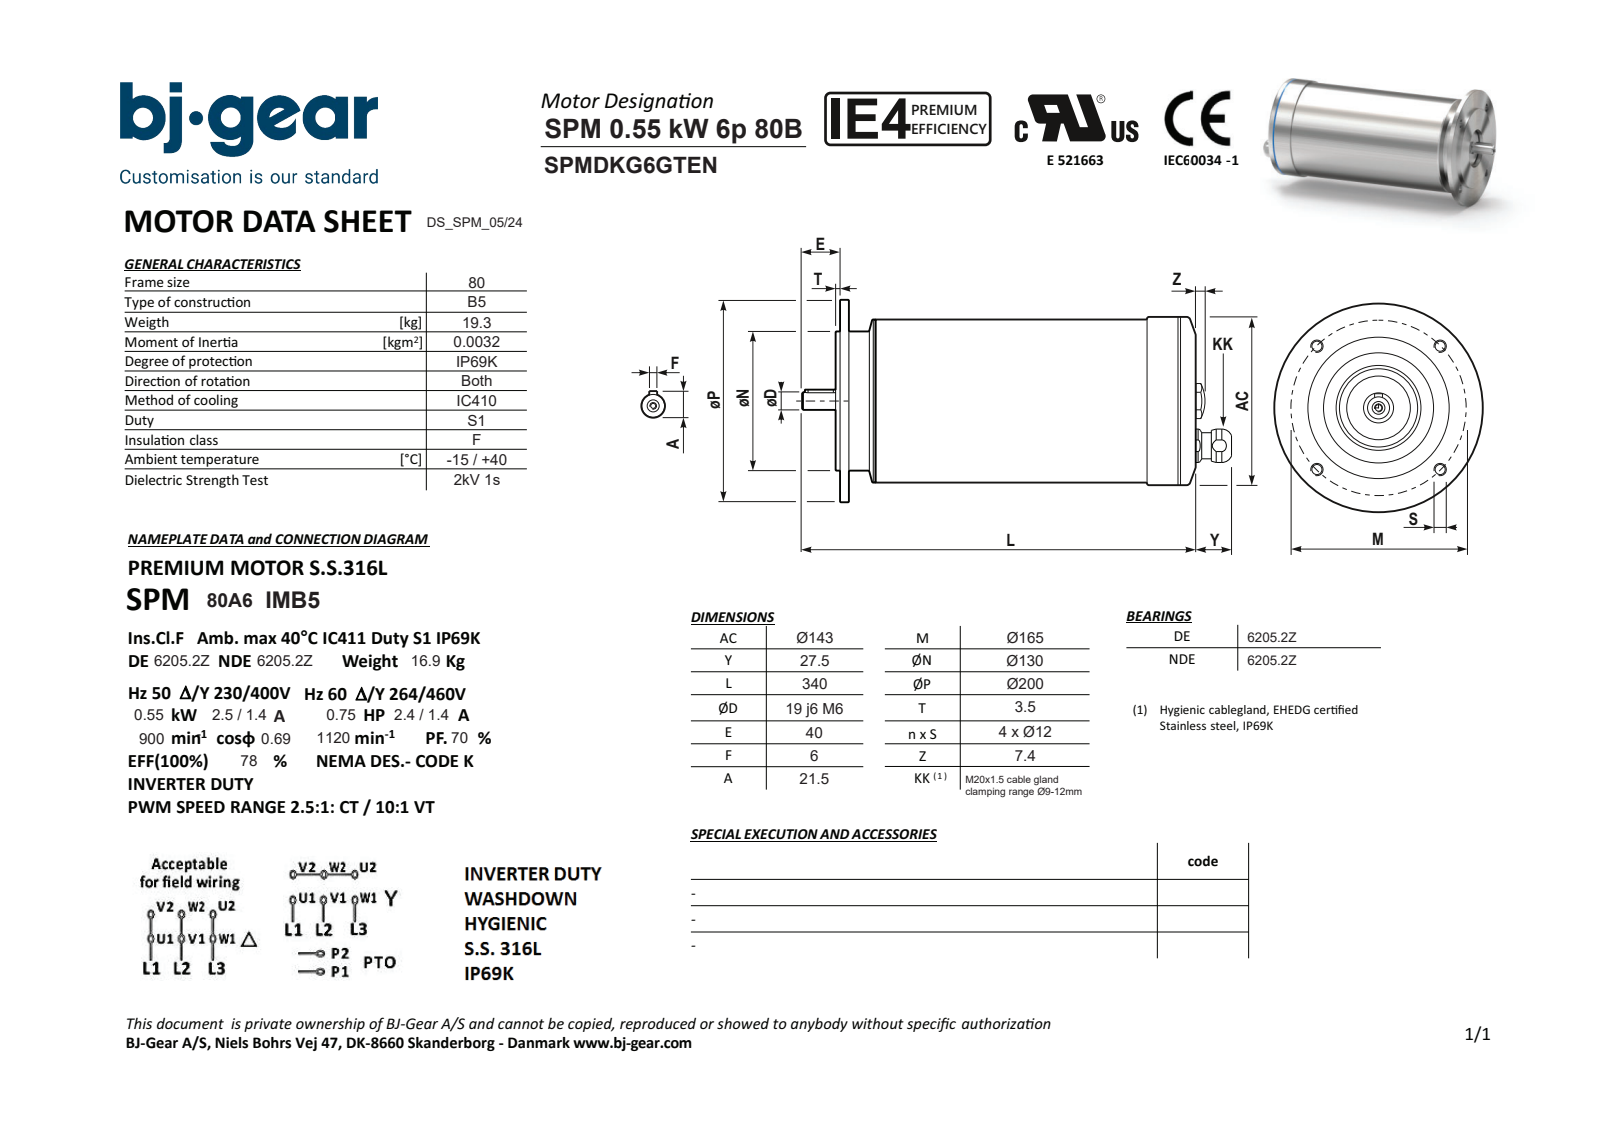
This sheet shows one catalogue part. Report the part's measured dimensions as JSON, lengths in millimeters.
{"part_name": "SPMDKG6GTENN4KSA1-N---NNN", "step_written_by": "Solid Edge (AUTOMOTIVE_DESIGN)", "units": "millimeters", "bodies": {"solids": 1, "faces": 79, "planar": 30, "cylindrical": 28, "other": 21}, "overall_size": [367.5, 200, 200], "volume_mm3": 4736000, "surface_area_mm2": 203697, "round_holes": [[12, 4], [4.92, 1], [6.4, 1], [7, 1], [13.4, 1], [68, 1]], "round_bosses_or_shafts": [[200, 1], [143, 1], [142.98, 1], [139, 1], [138.98, 1], [130, 1], [25, 1], [20, 1]], "partial_cylinders_radius": [[3, 2], [12.8, 1]], "face_to_face_distances": [8, 11.5, 3.5, 292, 300, 303.5, 6, 2, 294, 9.5], "hole_center_spacings": [82.51, 116.68, 61.78, 112.63, 165.01, 38]}
